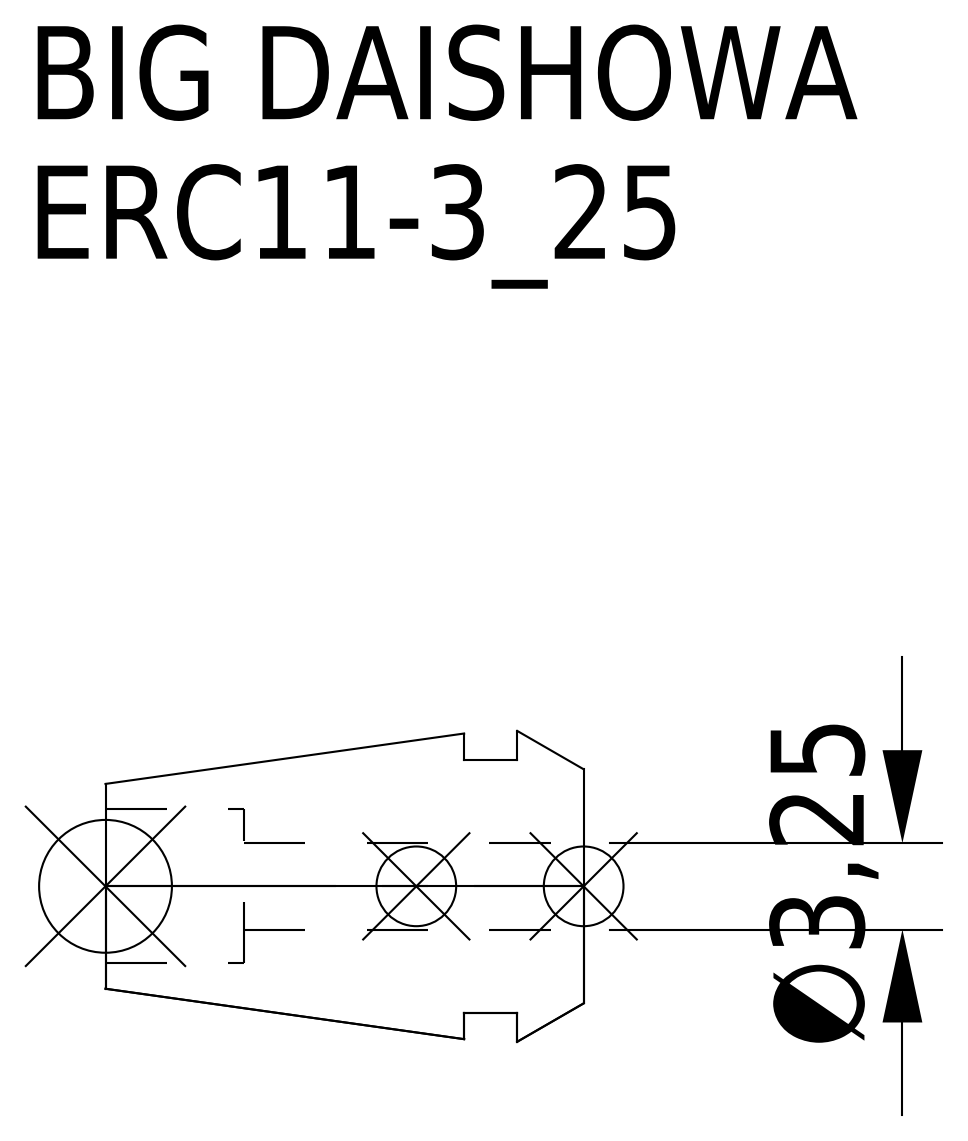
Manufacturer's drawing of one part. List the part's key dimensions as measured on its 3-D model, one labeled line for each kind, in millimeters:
Part name (STEP PRODUCT): ERC11-3_25
STEP written by: CREO PARAMETRIC BY PTC INC, 2016380 (AUTOMOTIVE_DESIGN)
Units: millimetres
Bodies: 1 solid, 15 faces (5 planar, 6 cylindrical, 4 other)
Overall size (bounding box): 18 × 11.7 × 11.7
Volume: 1 098 mm³ · Surface area: 951 mm²
Round holes (diameter × count): ⌀3.25 ×1, ⌀5.8 ×1
Round bosses / shafts (diameter × count): ⌀9.5 ×1
Main face-to-face distances: 2.5, 4.5, 2, 18, 15.5, 13.5, 12.79, 10.29, 8.29, 5.21
